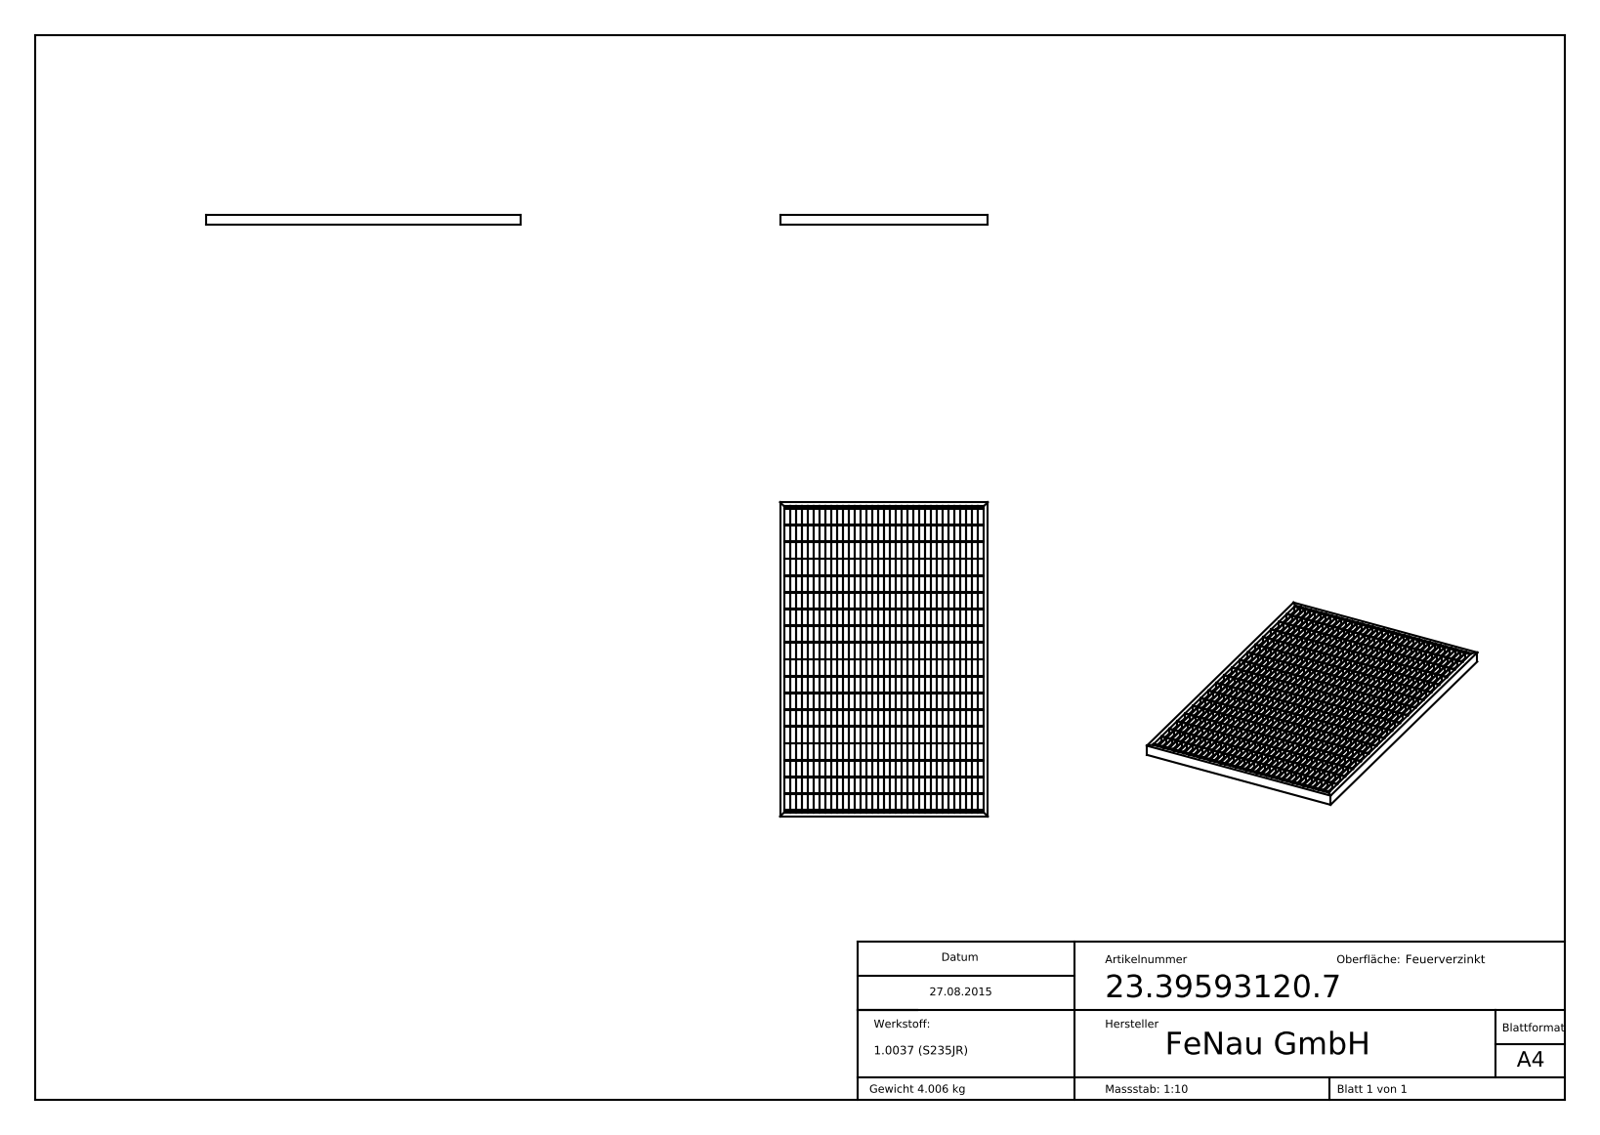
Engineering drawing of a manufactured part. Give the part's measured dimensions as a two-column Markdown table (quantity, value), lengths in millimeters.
| quantity | value |
| --- | --- |
| part name | 23-39593120-7 |
| STEP written by | SolidWorks 2015 (CONFIG_CONTROL_DESIGN) |
| units | millimeters |
| bodies | 1 solid, 2368 faces (2368 planar, 0 cylindrical, 0 other) |
| overall size | 590 × 390 × 20 |
| volume | 513 650 mm³ |
| surface area | 828 838 mm² |
| main face-to-face distances | 31.5, 63, 94.5, 126, 157.5, 189, 220.5, 11, 252, 22 |
